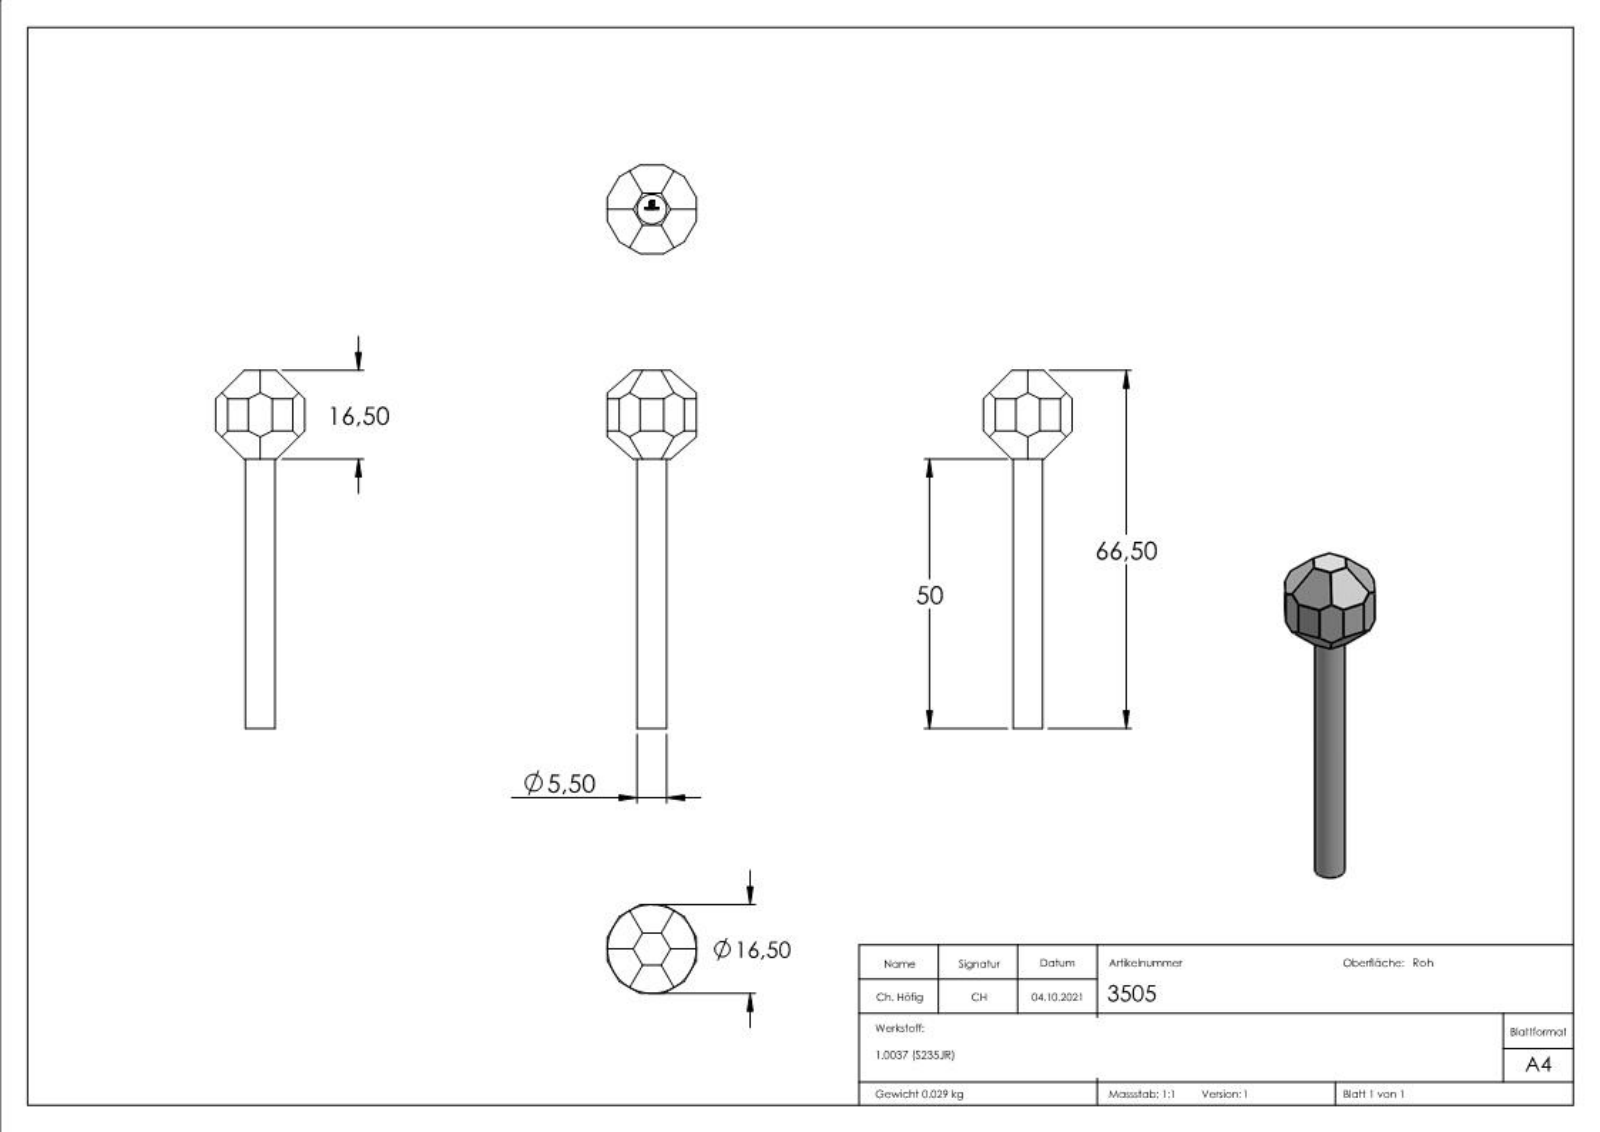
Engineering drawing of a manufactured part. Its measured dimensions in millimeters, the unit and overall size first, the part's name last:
Units: millimetres
Overall size (bounding box): 66.5 × 16.5 × 16.5
Round bosses / shafts (diameter × count): ⌀5.5 ×1
Main face-to-face distances: 15.9, 16.5, 66.5, 50, 49.9, 66.4, 0.88, 0.51, 0.65, 0.37
Volume: 3 723 mm³ · Surface area: 1 807 mm²
Bodies: 1 solid, 243 faces (135 planar, 1 cylindrical, 107 other)
Part name (STEP PRODUCT): 3505
STEP written by: SolidWorks 2018 (CONFIG_CONTROL_DESIGN)
